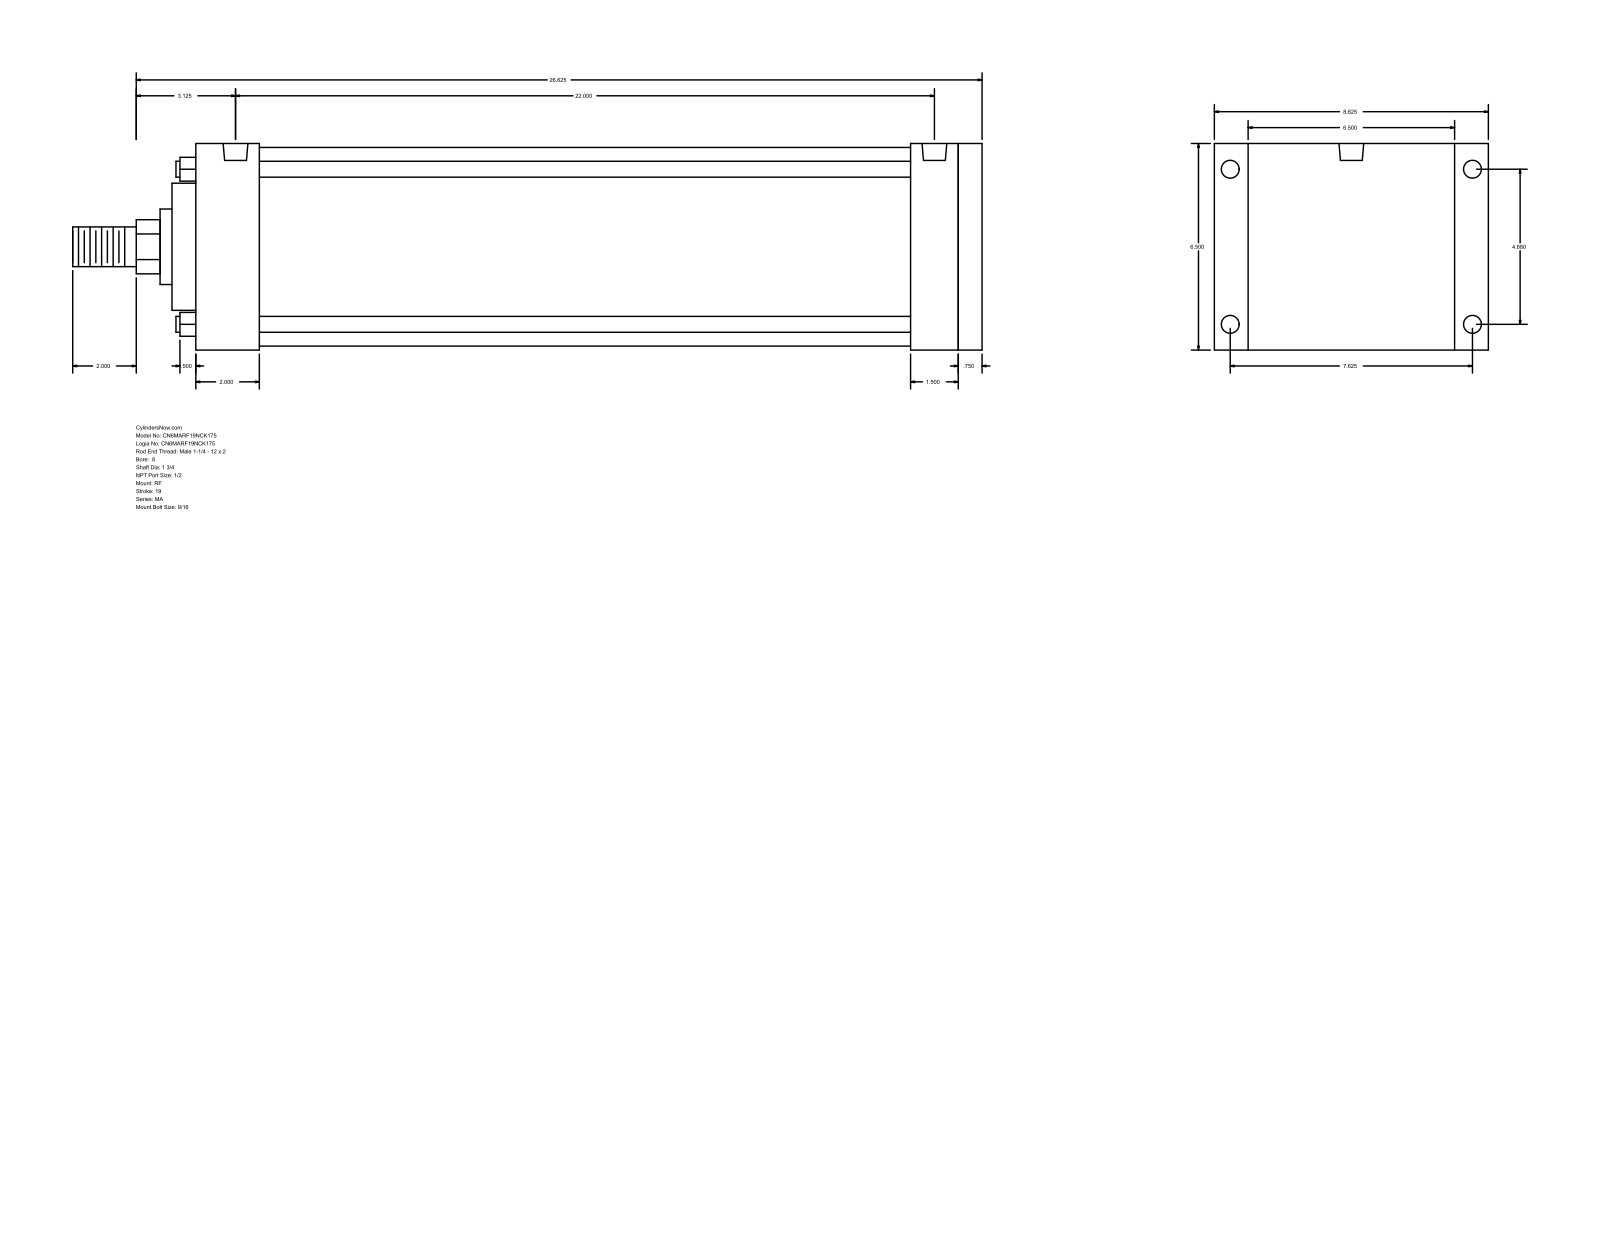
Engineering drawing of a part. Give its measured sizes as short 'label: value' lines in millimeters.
name: MA_RF__0600_1.75
written by: GSSL Pune (CONFIG_CONTROL_DESIGN)
unit: mm
bodies: 0 solids, 94 faces (65 planar, 29 cylindrical, 0 other)
size: 727.08 × 219.07 × 165.1
holes: 4× ⌀14.29, 4× ⌀17.46, 2× ⌀19.77
bosses: 4× ⌀12.7, 1× ⌀158.75, 1× ⌀101.6, 1× ⌀60.33, 1× ⌀44.45, 1× ⌀31.75
rounds: 1× R21.63
face distances: 165.1, 628.65, 19.04, 609.61, 50.8, 19.05, 558.81, 577.85, 571.5, 520.7
hole spacings: 123.96, 193.68, 229.95, 558.79
